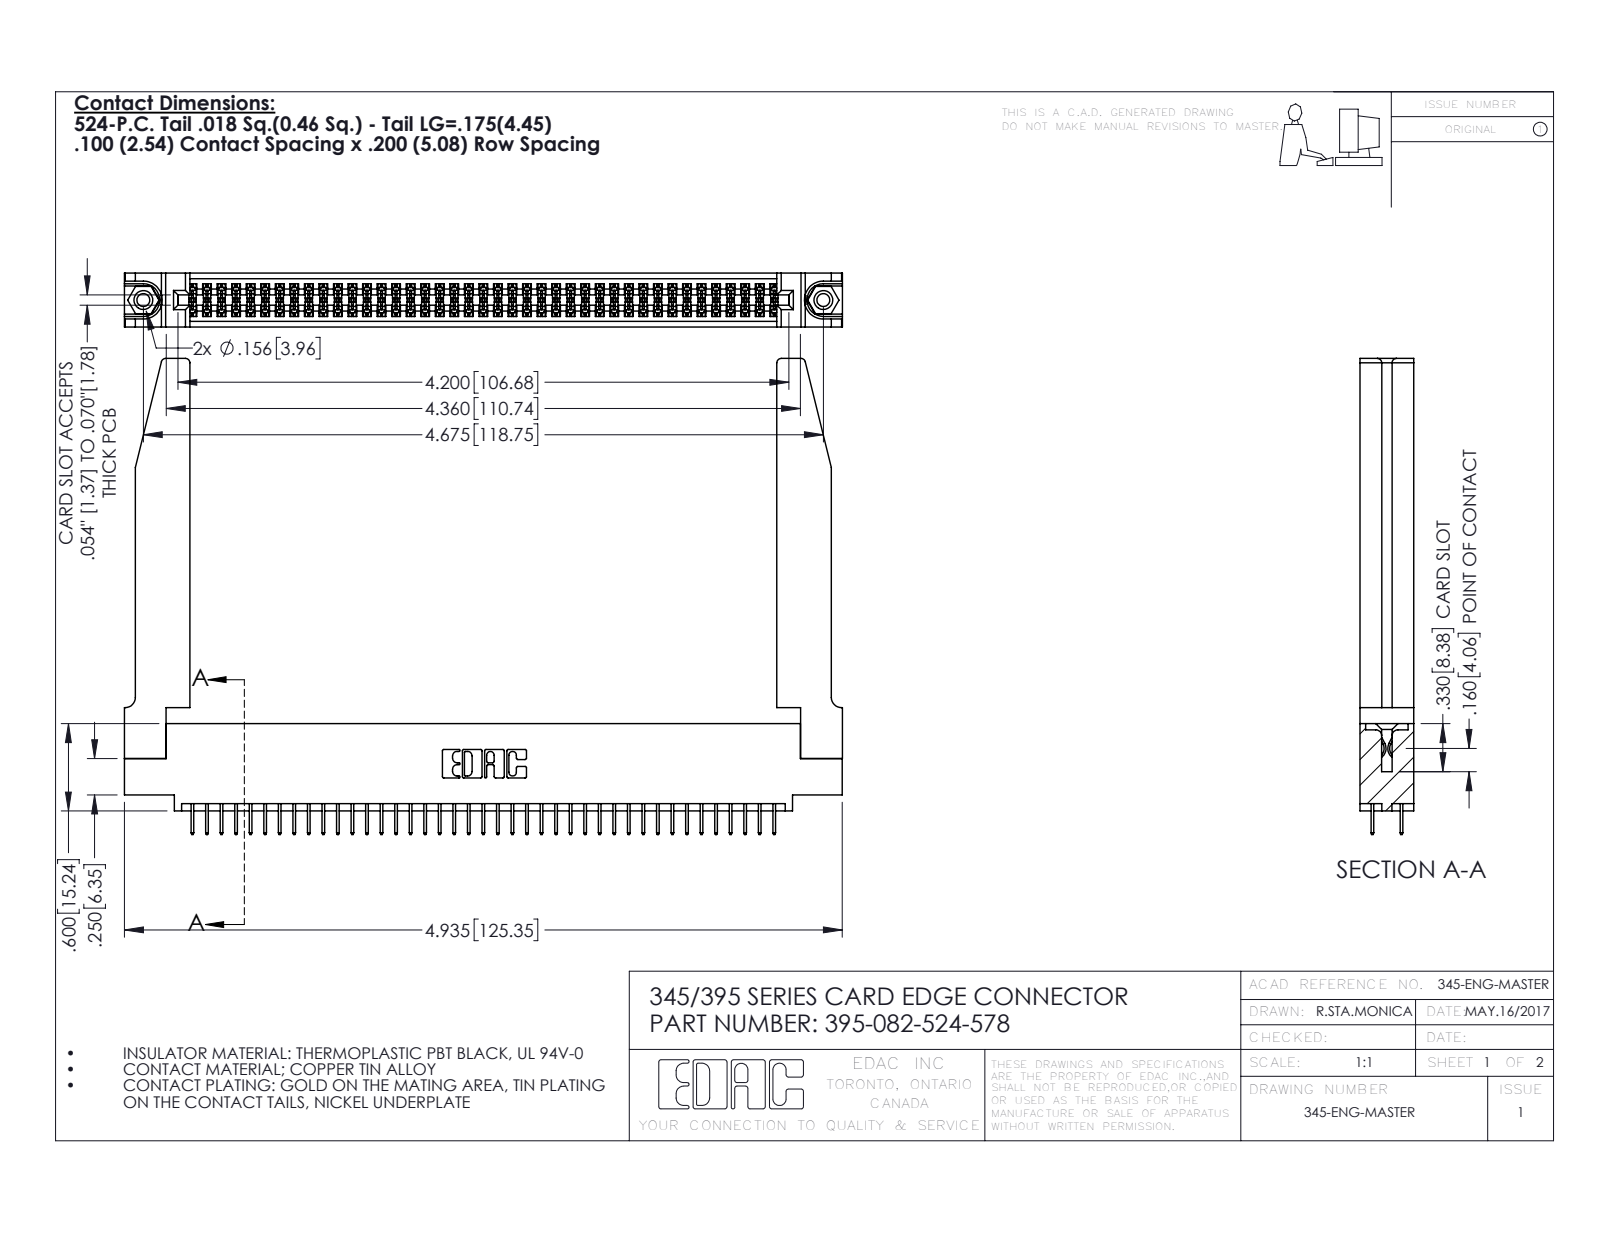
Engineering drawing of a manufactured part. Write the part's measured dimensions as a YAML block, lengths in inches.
part_name: "395-082-524-578; 345-220-078_345-220-078; 345 Part_0.110 Offset - 0.156 Dia-TH; 345-292-001_345-293-124 (+1 more)"
step_written_by: "SolidWorks 2016 (CONFIG_CONTROL_DESIGN)"
units: inches
bodies: {solids: 87, faces: 4792, planar: 3424, cylindrical: 1316, other: 52}
overall_size: [4.936, 3.272, 0.37]
volume: 1.205
surface_area: 37.64
round_holes:
  - {diameter: 0.089, count: 2}
  - {diameter: 0.125, count: 2}
  - {diameter: 0.156, count: 2}
  - {diameter: 0.064, count: 1}
round_bosses_or_shafts:
  - {diameter: 0.155, count: 2}
partial_cylinders:
  - {radius: 0.006, count: 123}
  - {radius: 0.01, count: 22}
  - {radius: 0.03, count: 8}
  - {radius: 0.007, count: 6}
  - {radius: 0.031, count: 6}
  - {radius: 0.026, count: 3}
  - {radius: 0.014, count: 2}
  - {radius: 0.019, count: 2}
face_to_face_distances: [0.37, 0.072, 0.298, 0.2, 0.098, 0.272, 0.025, 0.225, 0.148, 0.15]
hole_center_spacings: [0.27, 4.439, 4.675]
